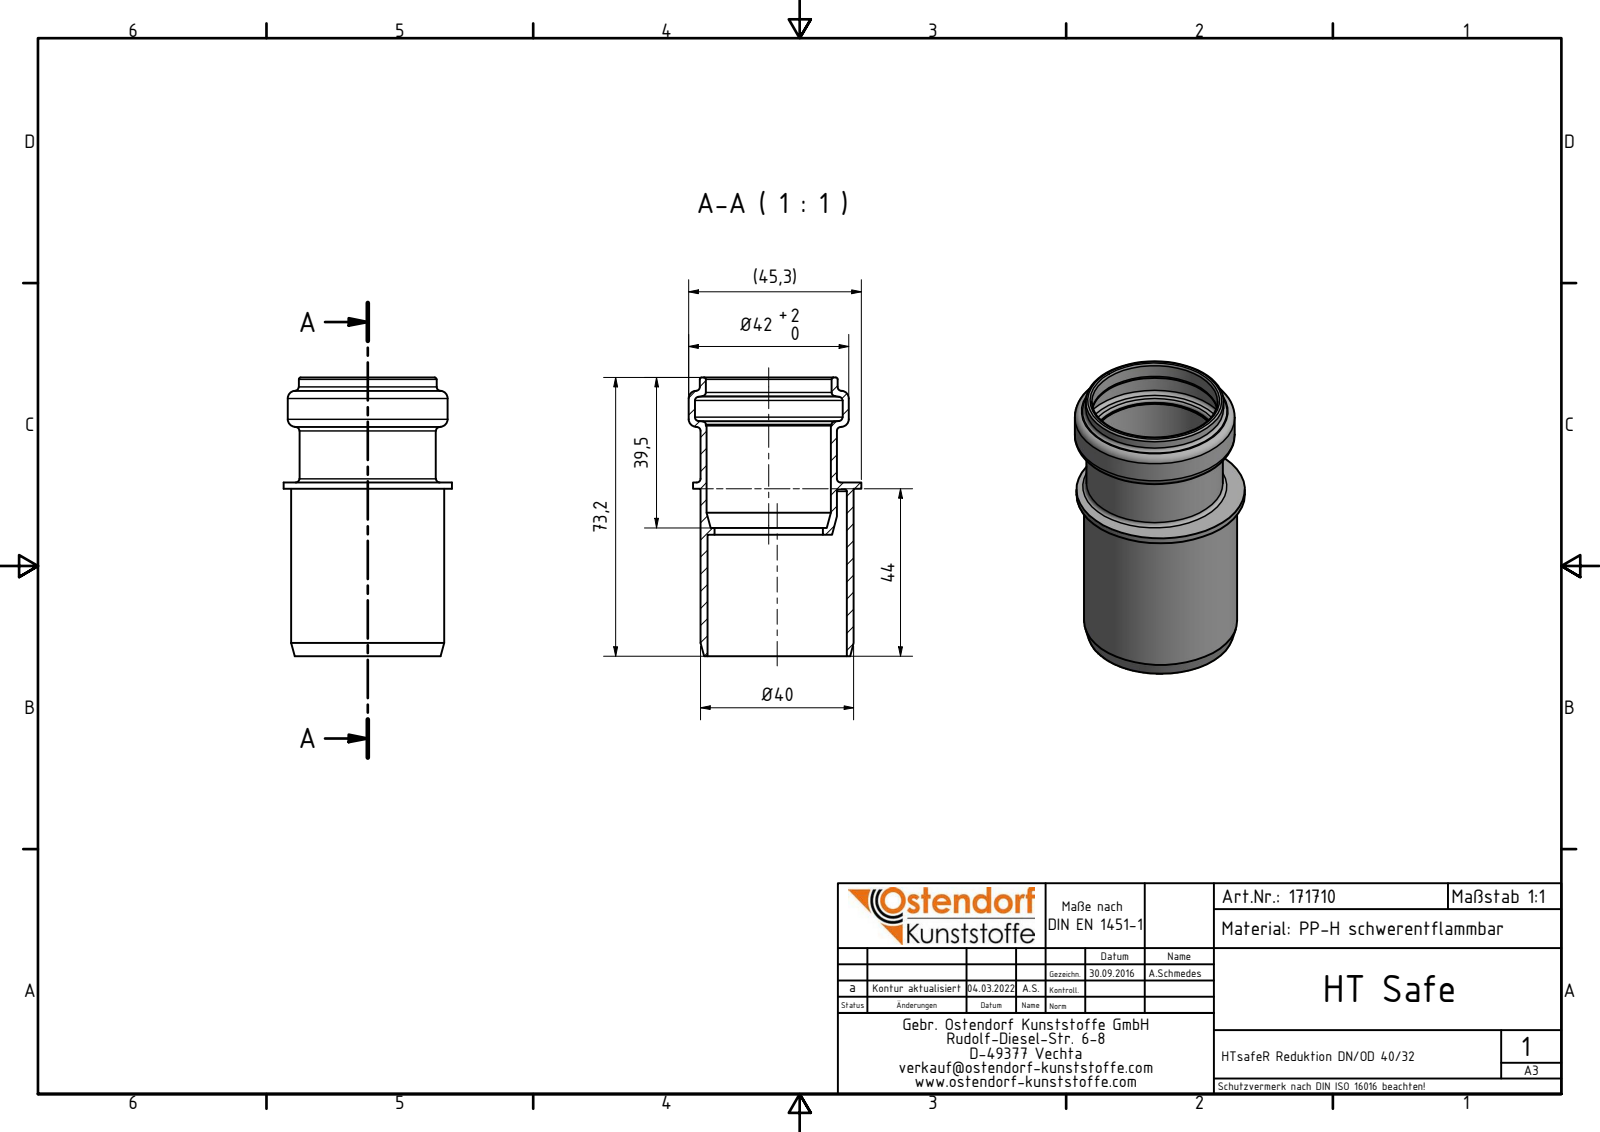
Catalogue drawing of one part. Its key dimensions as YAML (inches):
part_name: "171710 HTsafeR DN_OD 40_32"
step_written_by: "Autodesk Inventor 2020 (AUTOMOTIVE_DESIGN)"
units: inches
bodies: {solids: 1, faces: 40, planar: 8, cylindrical: 12, other: 20}
overall_size: [2.882, 1.783, 1.74]
volume: 1.106
surface_area: 32.47
round_holes:
  - {diameter: 1.118, count: 1}
  - {diameter: 1.283, count: 1}
  - {diameter: 1.299, count: 1}
  - {diameter: 1.441, count: 1}
  - {diameter: 1.528, count: 1}
round_bosses_or_shafts:
  - {diameter: 1.74, count: 1}
  - {diameter: 1.654, count: 1}
  - {diameter: 1.583, count: 1}
  - {diameter: 1.425, count: 1}
  - {diameter: 1.409, count: 1}
face_to_face_distances: [0.063, 0.476, 0.539, 0.071, 0.469, 1.256, 1.732, 1.795, 1.327, 0.406]
hole_center_spacings: [0.087]
